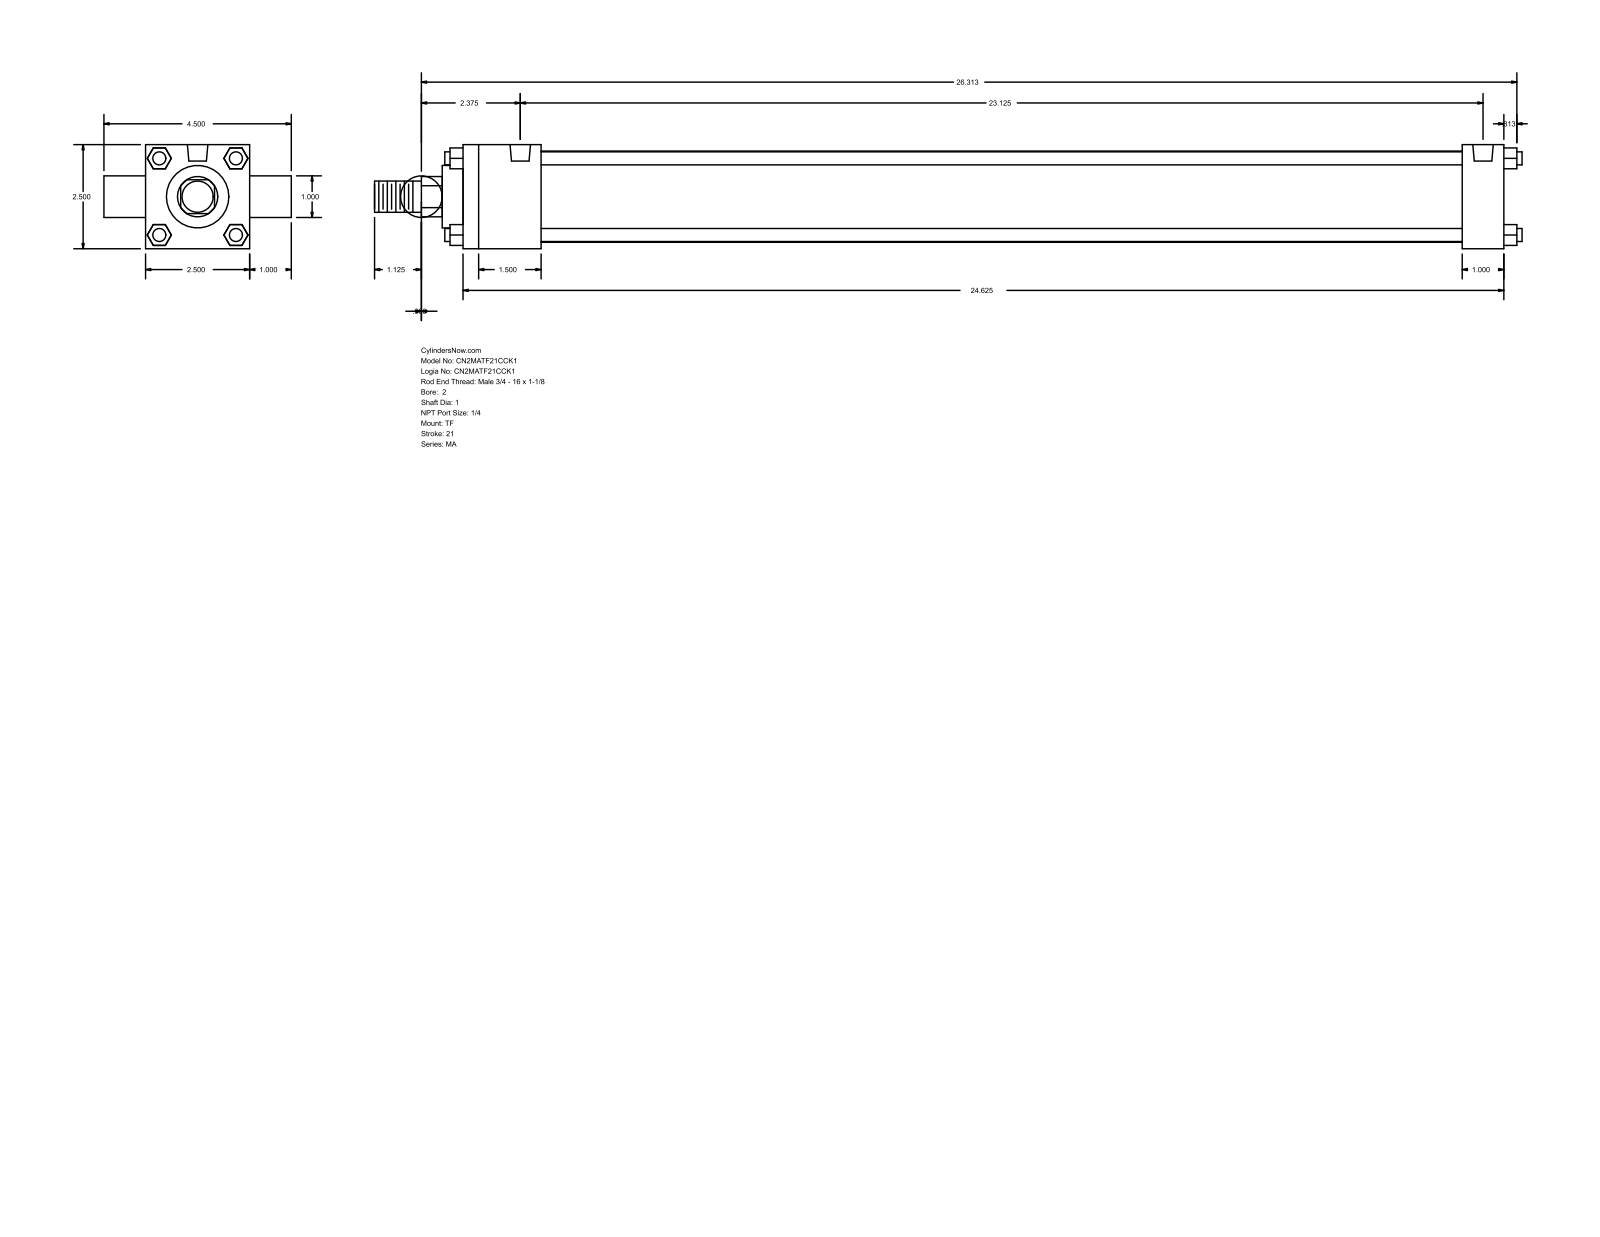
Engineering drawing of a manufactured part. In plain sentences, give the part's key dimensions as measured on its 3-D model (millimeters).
The part is named "MA_TF__0200_1". Its 3-D file was written by "GSSL Pune (CONFIG_CONTROL_DESIGN)". It is 0 solids with 120 faces: 92 planar, 28 cylindrical and 0 other. Overall it measures 700.09 by 114.3 by 63.5 millimeters. Round holes: 3 of diameter 7.94, 2 of diameter 12.49. Round bosses or shafts: 4 of diameter 7.94, 2 of diameter 25.4, 1 of diameter 55.63, 1 of diameter 38.1, 1 of diameter 19.05. Partial cylindrical surfaces (rounded edges, fillets, slot ends): 1 of radius 12.29. The main face-to-face distances are 63.5, 25.4, 635, 12.7, 47.63, 609.6, 561.97, 587.37, 88.9, 40.47. The hole center spacings are 587.37.
